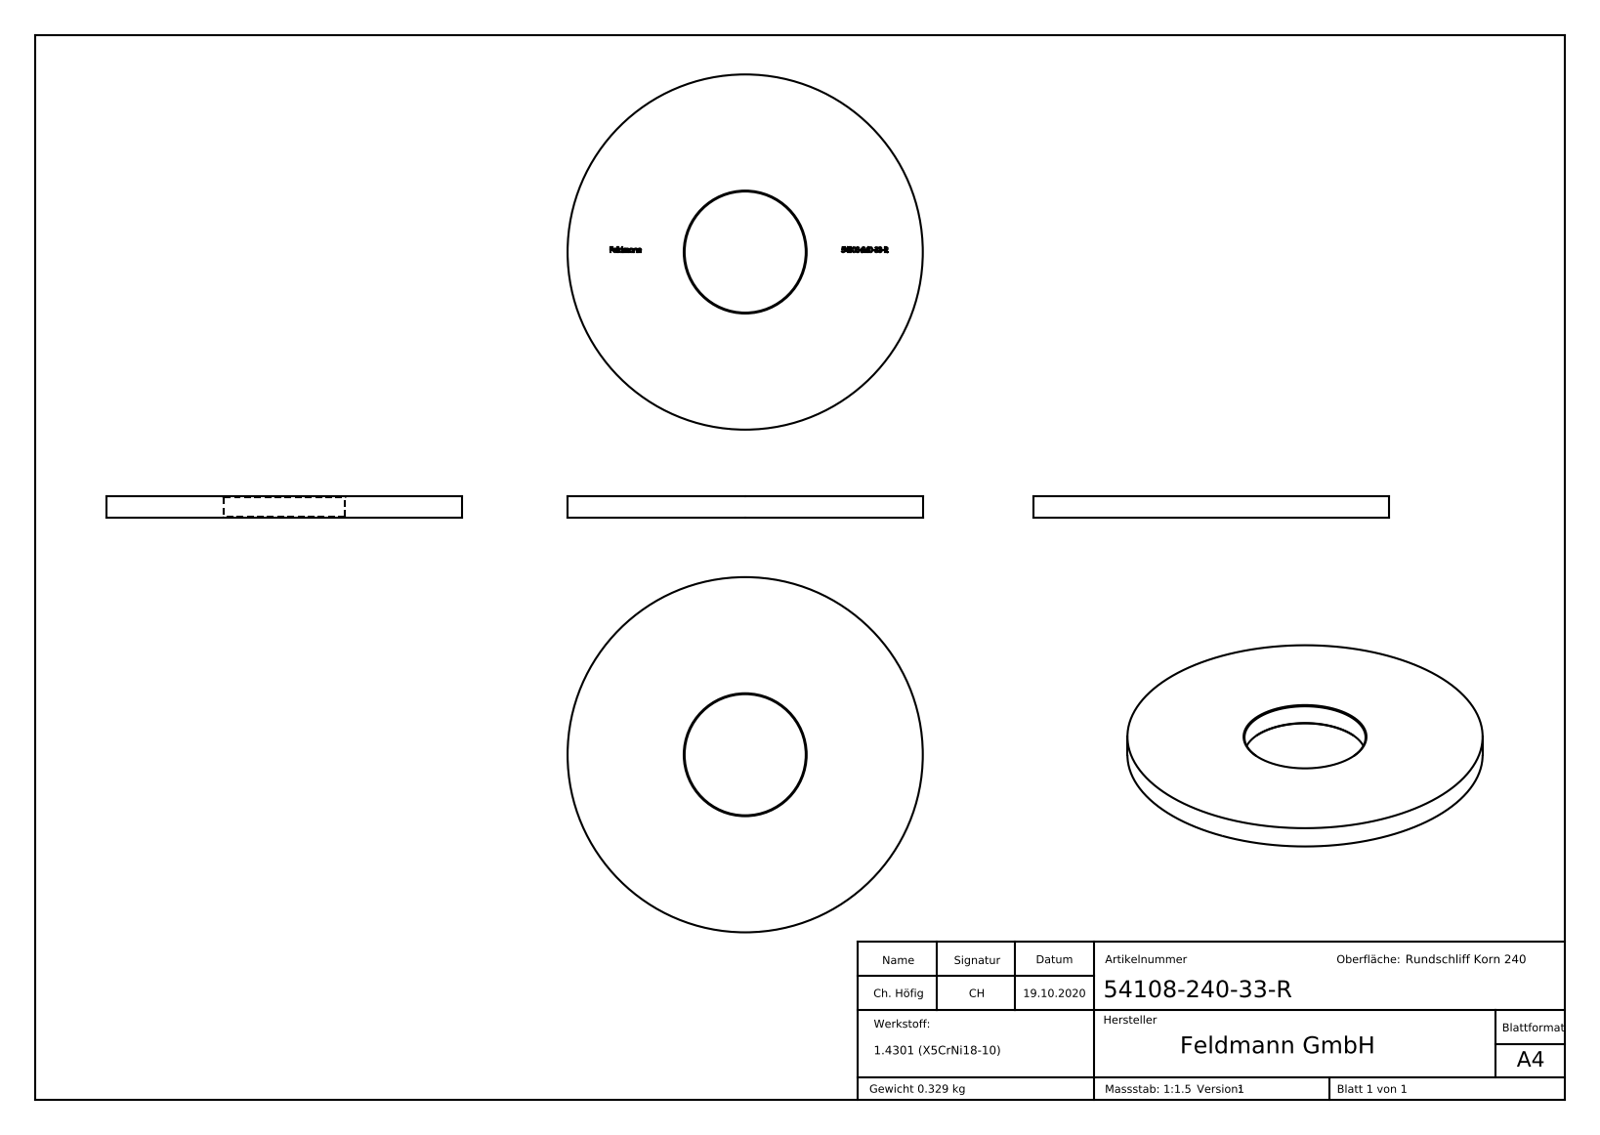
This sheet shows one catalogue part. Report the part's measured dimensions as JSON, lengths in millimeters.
{"part_name": "54108-240-33-R", "step_written_by": "SolidWorks 2018 (CONFIG_CONTROL_DESIGN)", "units": "millimeters", "bodies": {"solids": 1, "faces": 299, "planar": 161, "cylindrical": 4, "other": 134}, "overall_size": [100, 100, 6], "volume_mm3": 41637, "surface_area_mm2": 16390, "round_holes": [[34.1, 1]], "round_bosses_or_shafts": [[100, 1]], "face_to_face_distances": [6, 5.9, 0.44, 0.88, 0.58, 4.9, 4.78, 77.19, 67.51, 9.68]}
